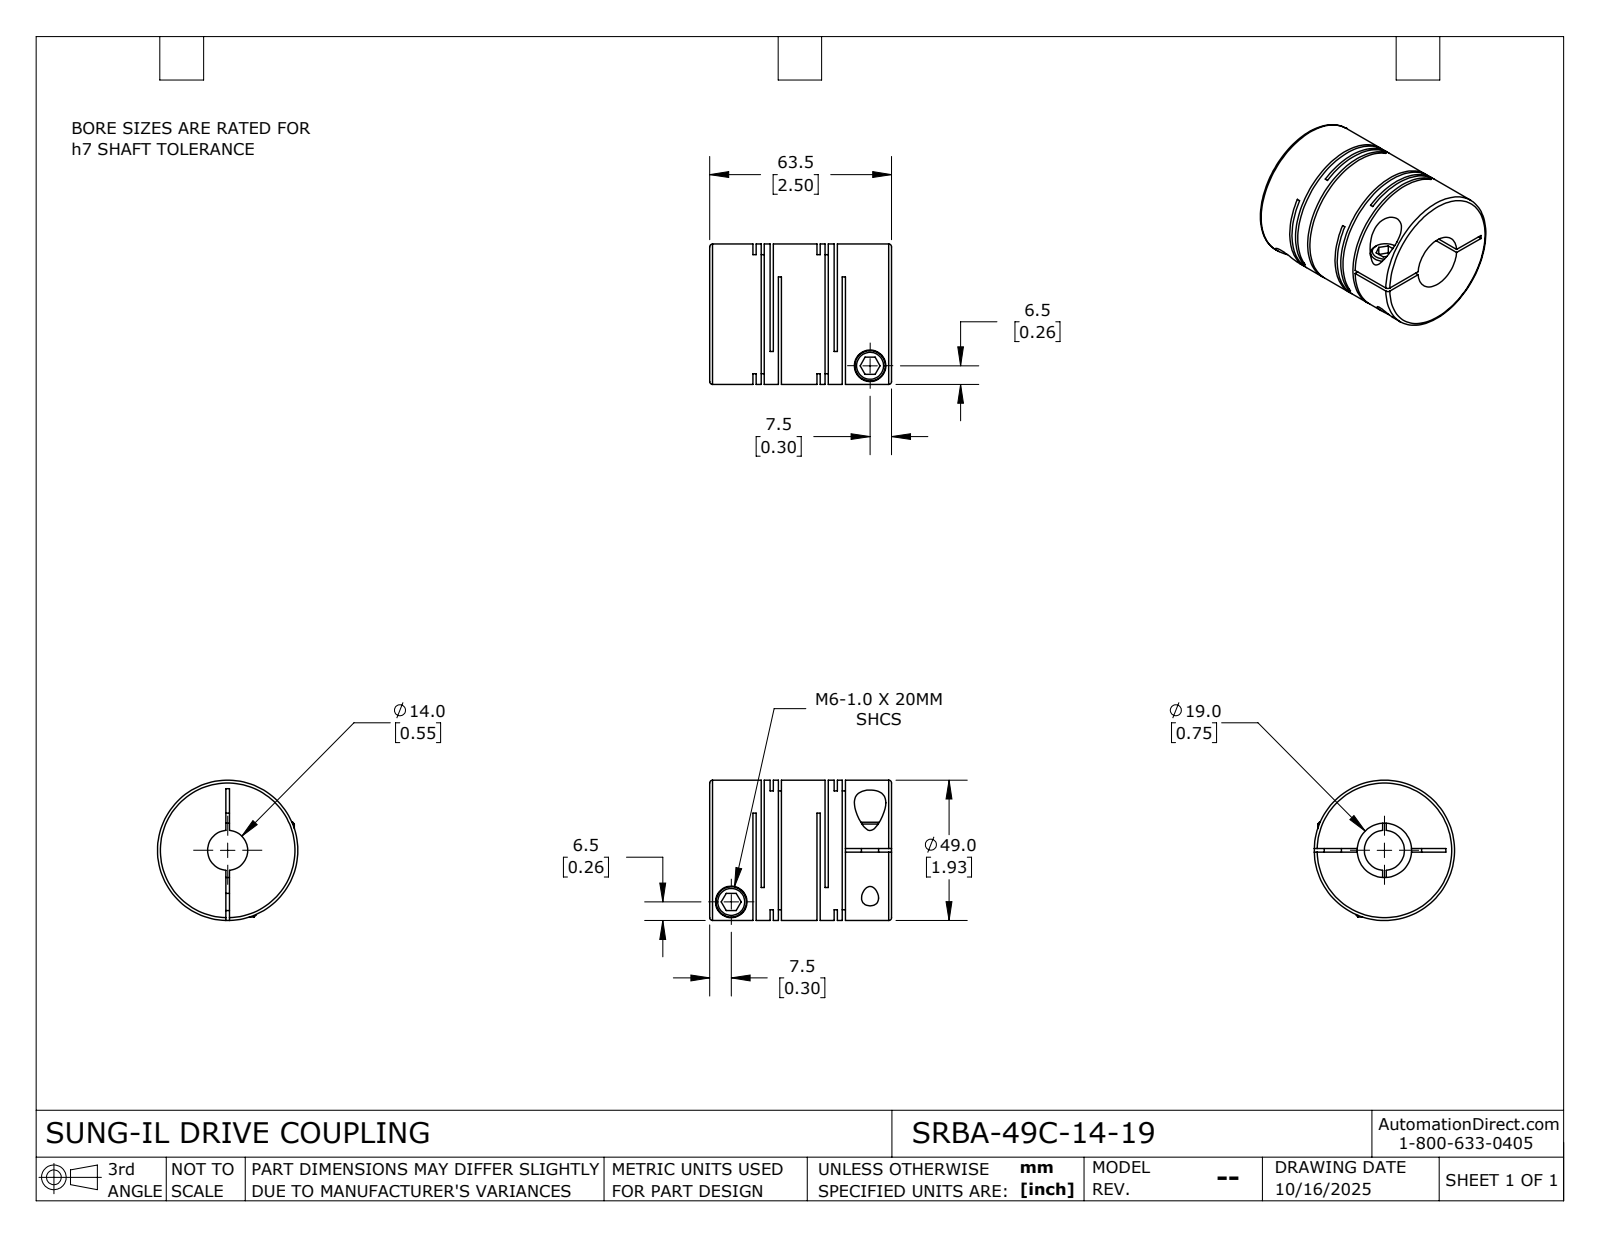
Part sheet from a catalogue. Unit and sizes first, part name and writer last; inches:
Units: inches
Overall size (bounding box): 2.5 × 1.929 × 1.929
Round holes (diameter × count): ⌀0.236 ×2, ⌀0.433 ×2, ⌀0.551 ×1, ⌀0.748 ×1
Round bosses / shafts (diameter × count): ⌀0.417 ×2, ⌀1.929 ×1
Main face-to-face distances: 0.236, 0.043, 0.88, 0.112, 0.837, 0.124, 0.069, 0.193, 0.768, 0.644
Volume: 5.474 in³ · Surface area: 59.79 in²
Bodies: 1 solid, 115 faces (60 planar, 42 cylindrical, 13 other)
Part name (STEP PRODUCT): SRBA-49C-14-19
STEP written by: SolidWorks 2024 (CONFIG_CONTROL_DESIGN)
